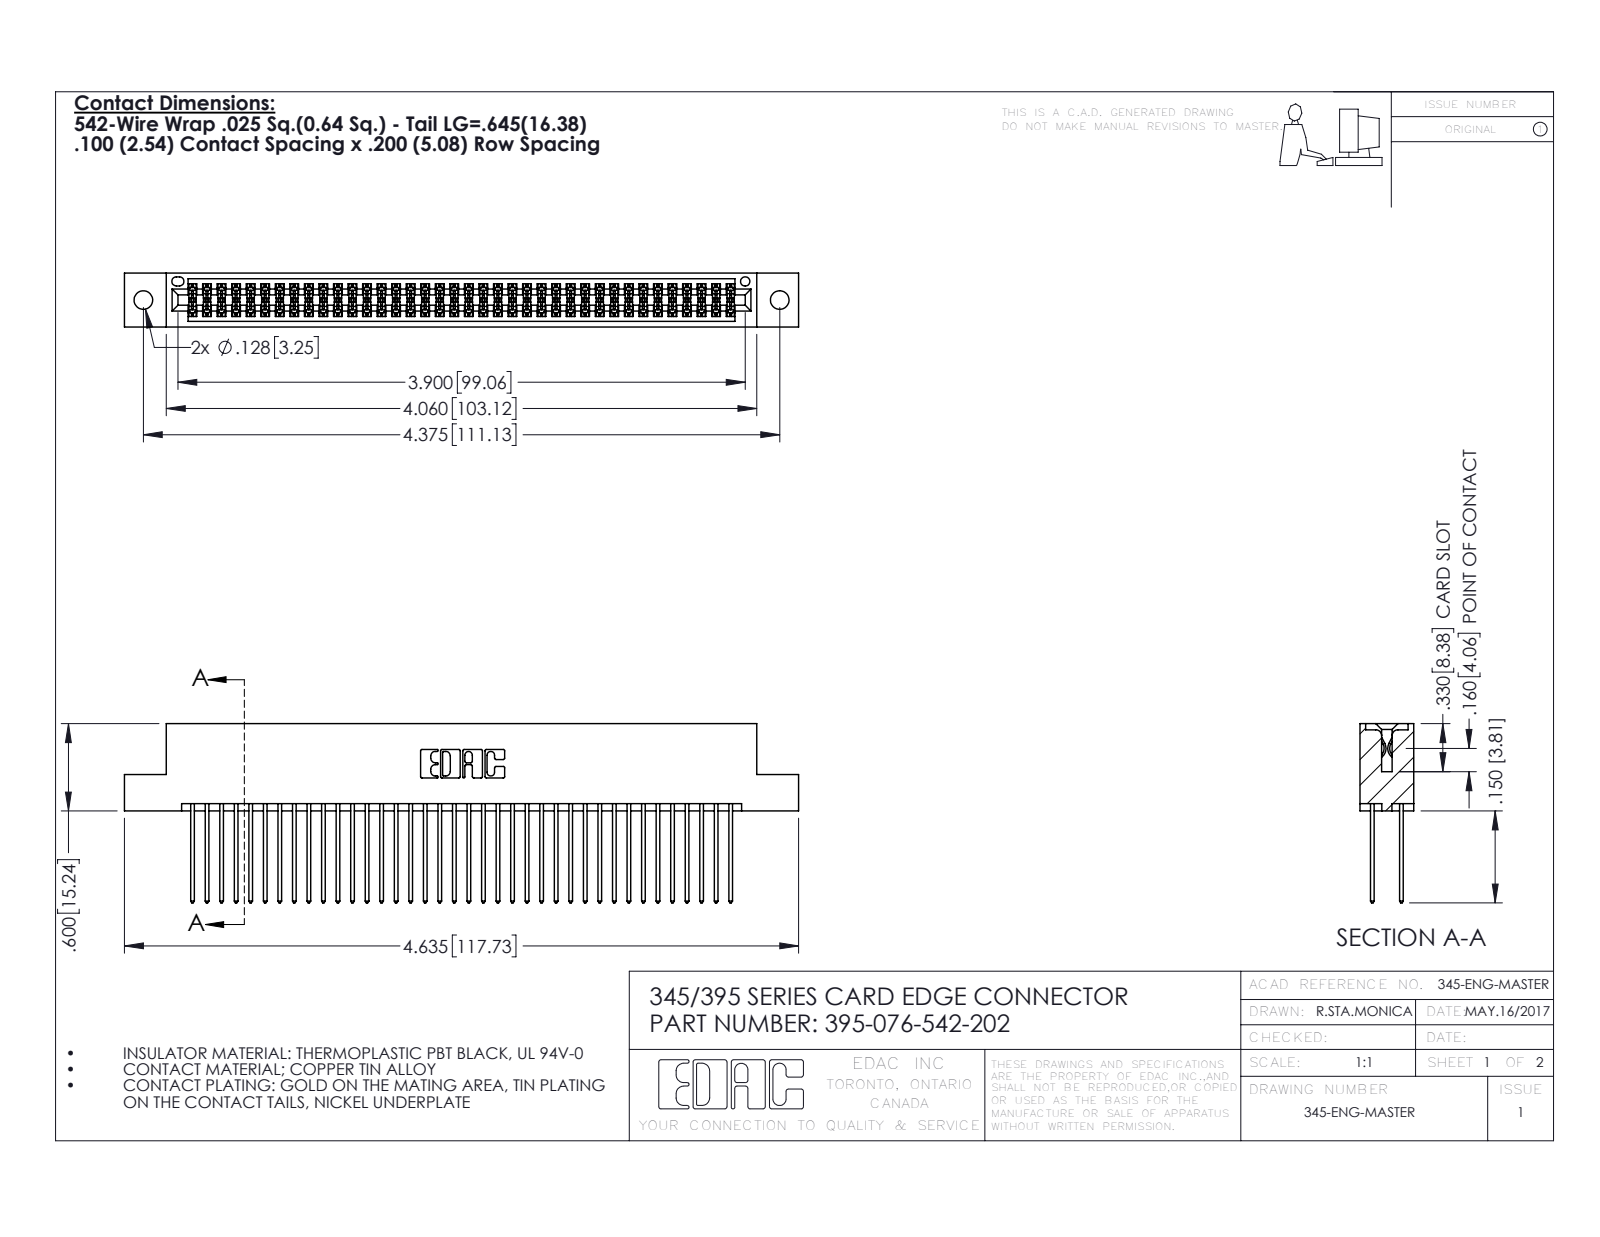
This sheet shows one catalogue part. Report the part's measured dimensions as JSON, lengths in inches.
{"part_name": "345 Part_Flush Mounting Lugs - 0.128 Dia; 395-076-542-202; 345-292-001_345-293-142", "step_written_by": "SolidWorks 2016 (CONFIG_CONTROL_DESIGN)", "units": "inches", "bodies": {"solids": 77, "faces": 3926, "planar": 2588, "cylindrical": 1338, "other": 0}, "overall_size": [4.635, 1.232, 0.37], "volume_in3": 0.715, "surface_area_in2": 28.87, "round_holes": [[0.128, 2], [0.064, 1]], "partial_cylinders_radius": [[0.006, 114], [0.01, 76], [0.01, 22], [0.007, 6], [0.031, 6], [0.026, 3], [0.014, 2], [0.019, 2]], "face_to_face_distances": [0.298, 0.072, 0.2, 0.098, 0.272, 0.025, 0.37, 0.225, 0.175, 0.149], "hole_center_spacings": [0.27, 4.139, 4.375]}
